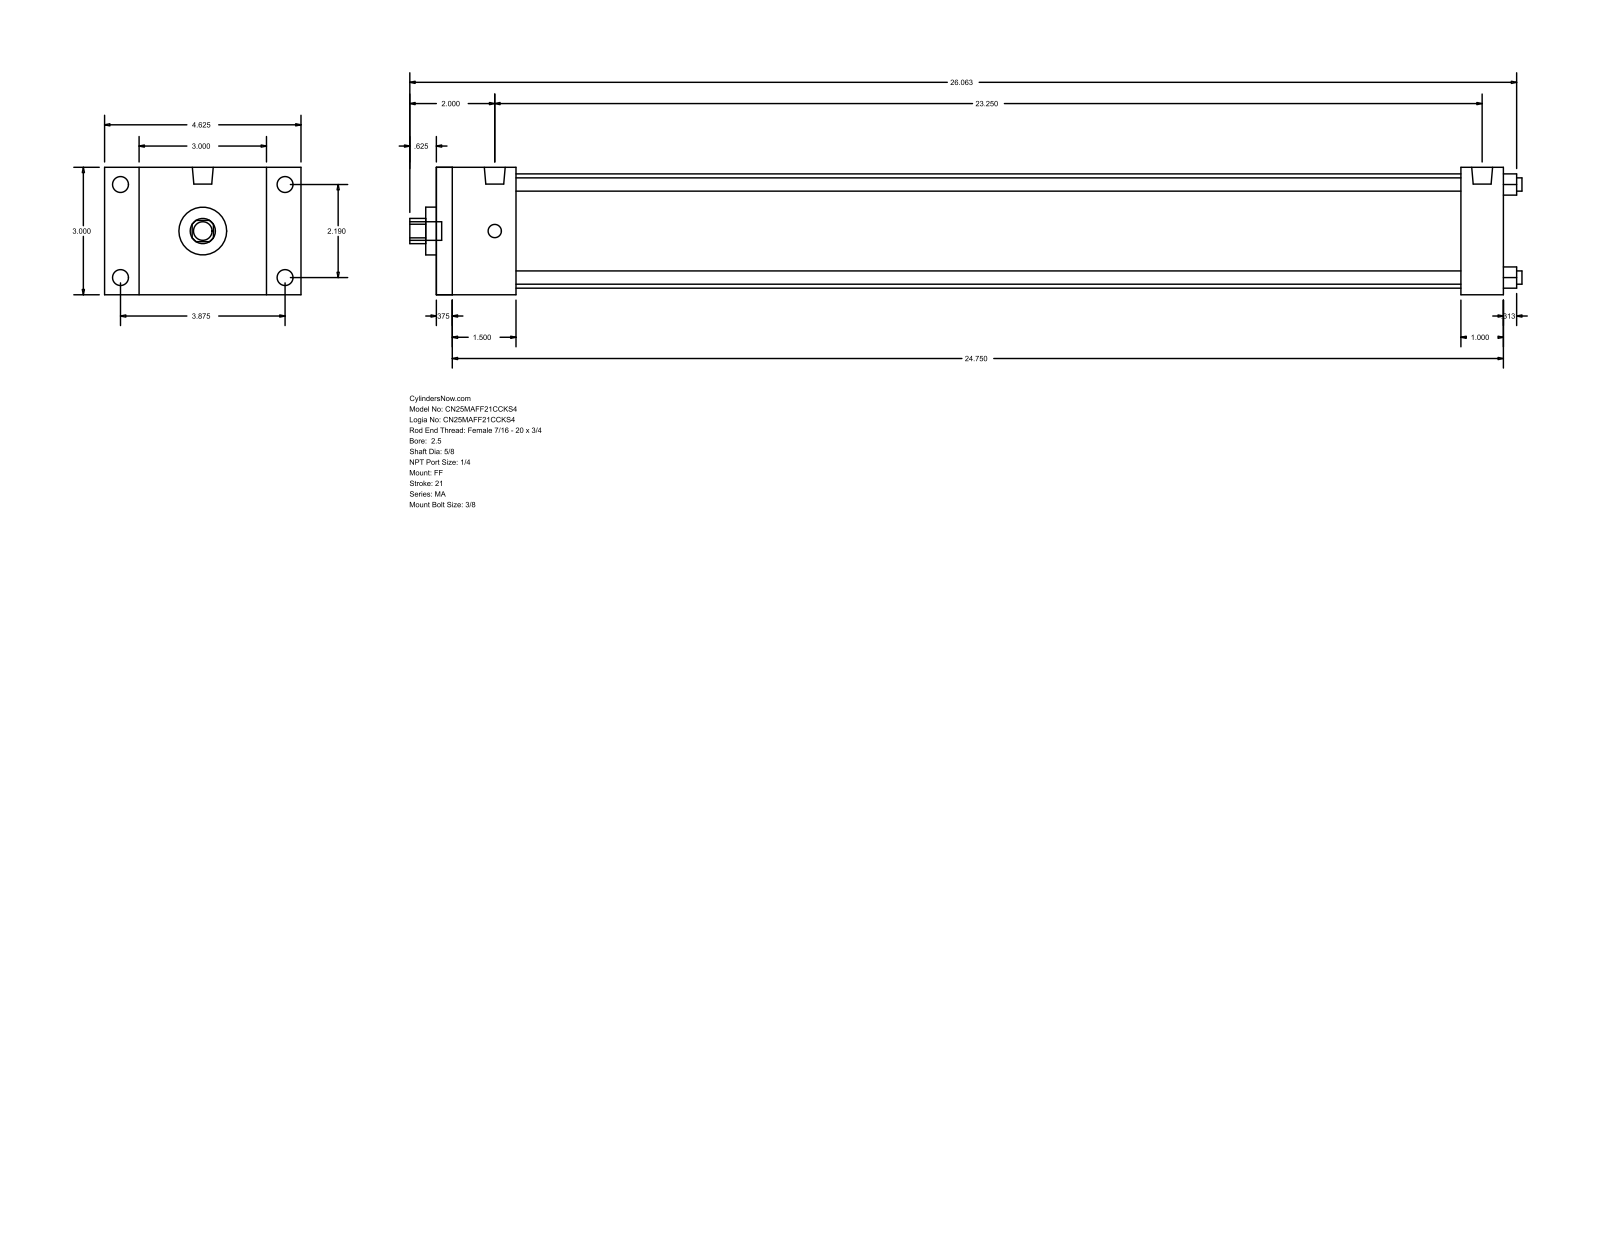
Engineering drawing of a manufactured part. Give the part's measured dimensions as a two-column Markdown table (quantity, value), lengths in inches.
| quantity | value |
| --- | --- |
| part name | MA_FF__0250_0.625 |
| STEP written by | GSSL Pune (CONFIG_CONTROL_DESIGN) |
| units | inches |
| bodies | 0 solids, 92 faces (64 planar, 28 cylindrical, 0 other) |
| overall size | 26.187 × 4.625 × 3 |
| round holes (diameter × count) | 0.313 × 4, 0.625 × 1, 1.125 × 1, 2.69 × 1 |
| round bosses / shafts (diameter × count) | 0.375 × 4, 0.313 × 4, 0.492 × 2, 0.437 × 1 |
| partial cylindrical surfaces (radius × count) | 0.297 × 1 |
| main face-to-face distances | 3, 25.125, 0.375, 24.75, 1, 1.875, 24.125, 1.5, 23.75, 22.25 |
| hole center spacings | 1.548, 2.19, 3.097 |
